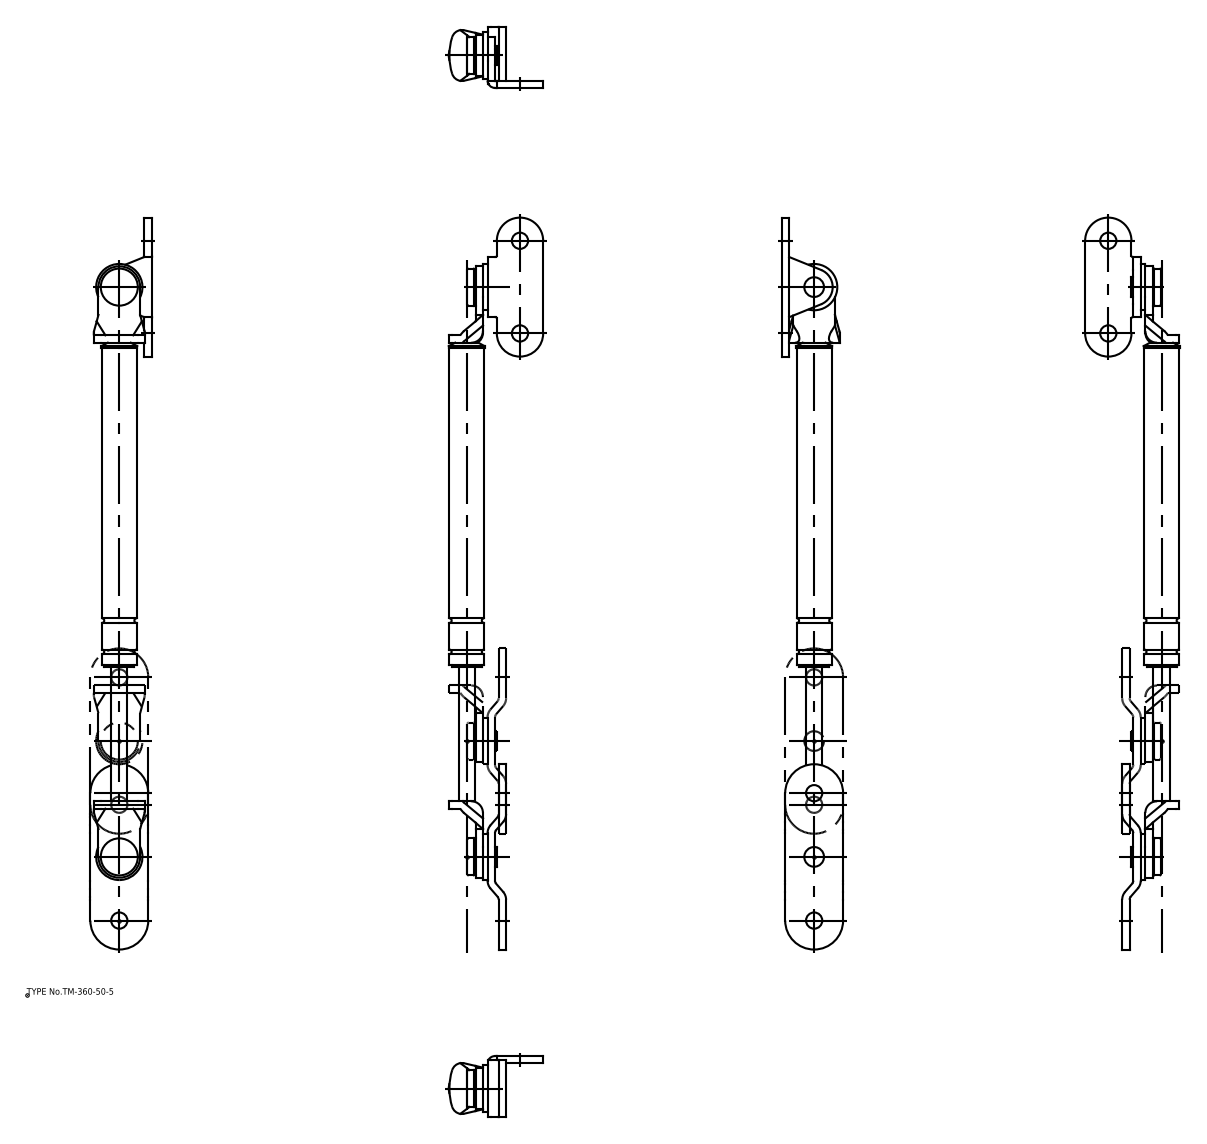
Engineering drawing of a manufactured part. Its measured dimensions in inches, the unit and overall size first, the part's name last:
Units: inches
Overall size (bounding box): 12.441 × 1.604 × 1.043
Round holes (diameter × count): ⌀0.276 ×4, ⌀0.335 ×2, ⌀0.394 ×2
Round bosses / shafts (diameter × count): ⌀0.787 ×2, ⌀0.63 ×2, ⌀0.61 ×1, ⌀0.591 ×1, ⌀0.512 ×1, ⌀0.276 ×1
Partial cylindrical surfaces — rounded edges, fillets, slot ends (radius × count): R0.079 ×4, R0.205 ×4, R0.02 ×2, R0.173 ×2, R0.197 ×2, R0.354 ×2, R0.394 ×2, R0.492 ×2
Main face-to-face distances: 0.126, 0.205, 0.394, 0.189, 0.079, 0.52, 0.268, 0.315, 0.331, 0.063
Hole centre spacings: 1.083, 1.575, 2.165, 8.602, 9.685, 10.768
Volume: 2.728 in³ · Surface area: 36.24 in²
Bodies: 10 solids, 167 faces (71 planar, 80 cylindrical, 16 other)
Part name (STEP PRODUCT): ワッシャー; ウェーブワッシャー; ブラケット(A); ボルト (+3 more)
STEP written by: spGate 16.7.1 (AUTOMOTIVE_DESIGN)
